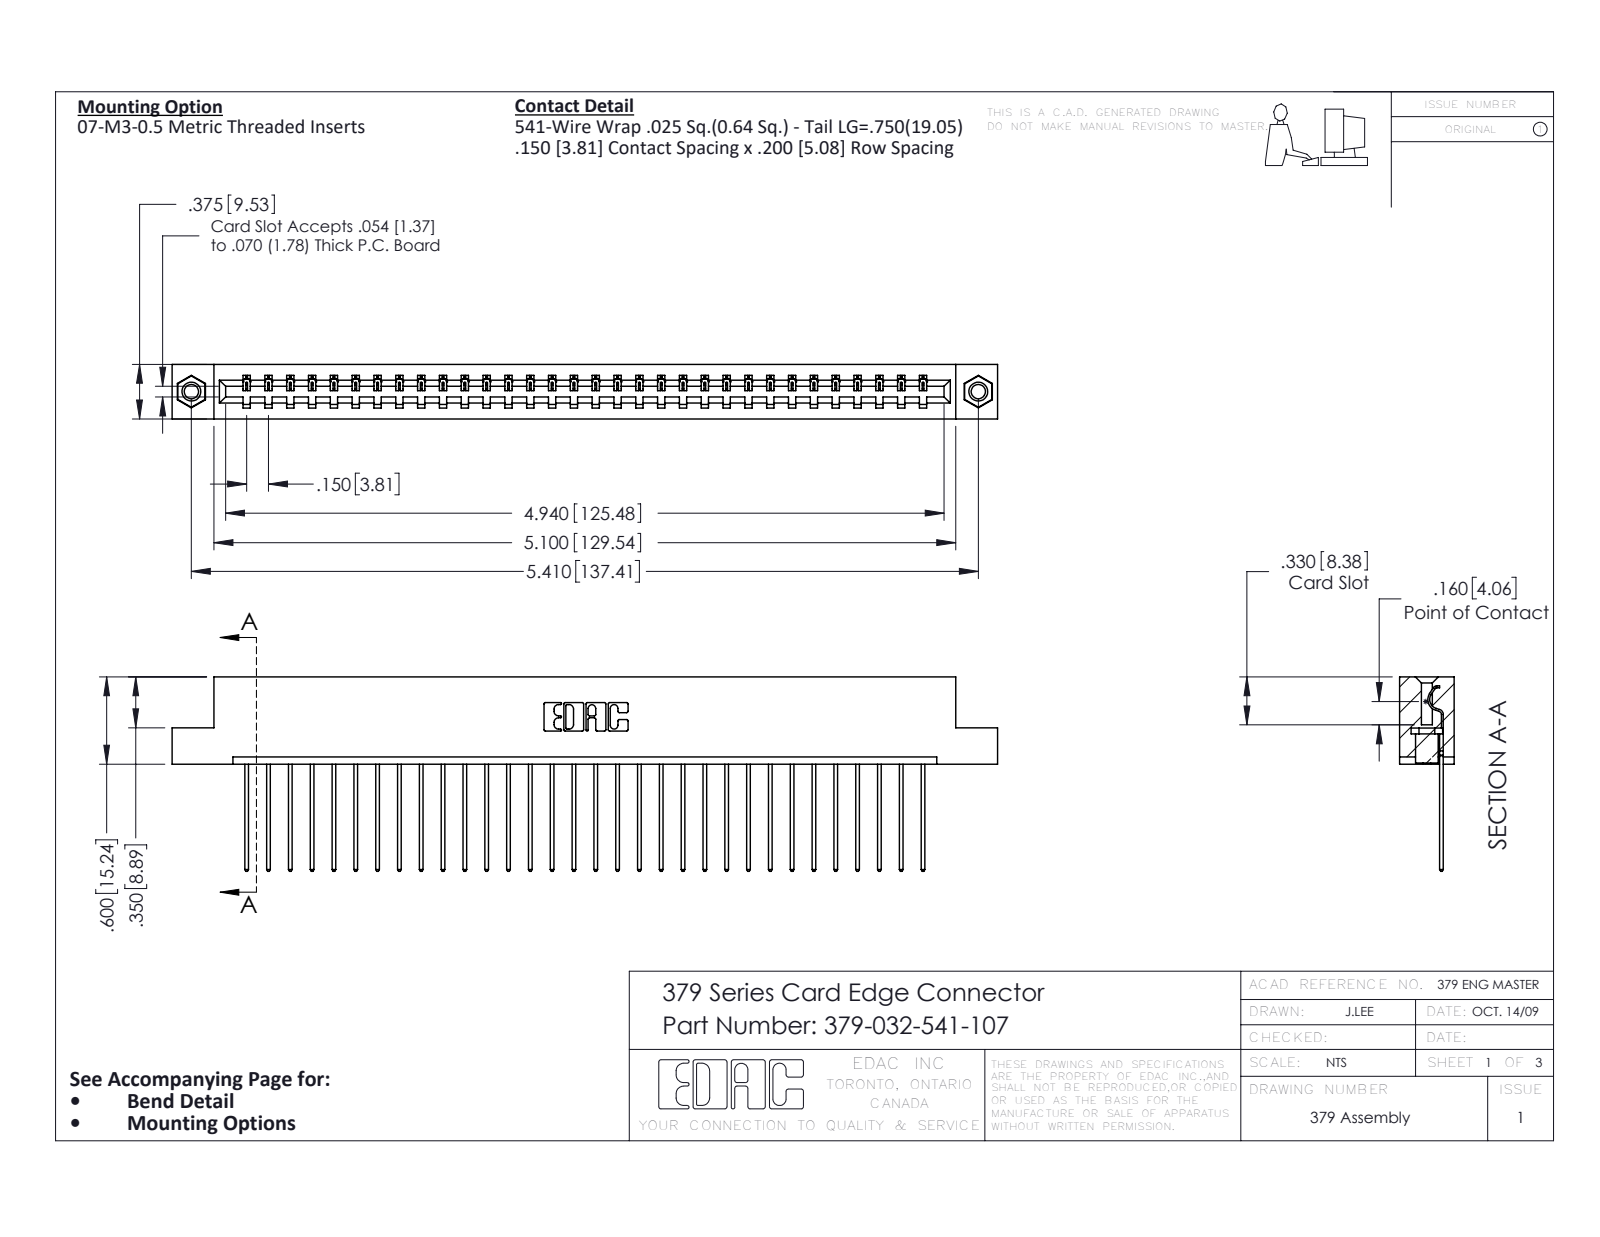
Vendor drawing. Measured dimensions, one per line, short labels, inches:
name: 379-032-541-107; 345-250-001_345-250-005-103; 379 Part_Flush - .156 Dia - TI; 345-292-001_345-293-141
written by: SolidWorks 2016 (CONFIG_CONTROL_DESIGN)
unit: in
bodies: 35 solids, 2030 faces (1446 planar, 568 cylindrical, 16 other)
size: 5.675 × 1.337 × 0.375
volume: 0.922 in³; area: 24.97 in²
holes: 2× ⌀0.098, 2× ⌀0.125, 2× ⌀0.156
bosses: 2× ⌀0.155
rounds: 64× R0.006, 64× R0.01, 22× R0.01, 6× R0.007, 6× R0.031, 3× R0.026, 1× R0.014, 1× R0.022
face distances: 0.3, 0.075, 0.375, 0.225, 0.275, 0.1, 0.025, 0.2, 0.6, 0.55
hole spacings: 5.41
